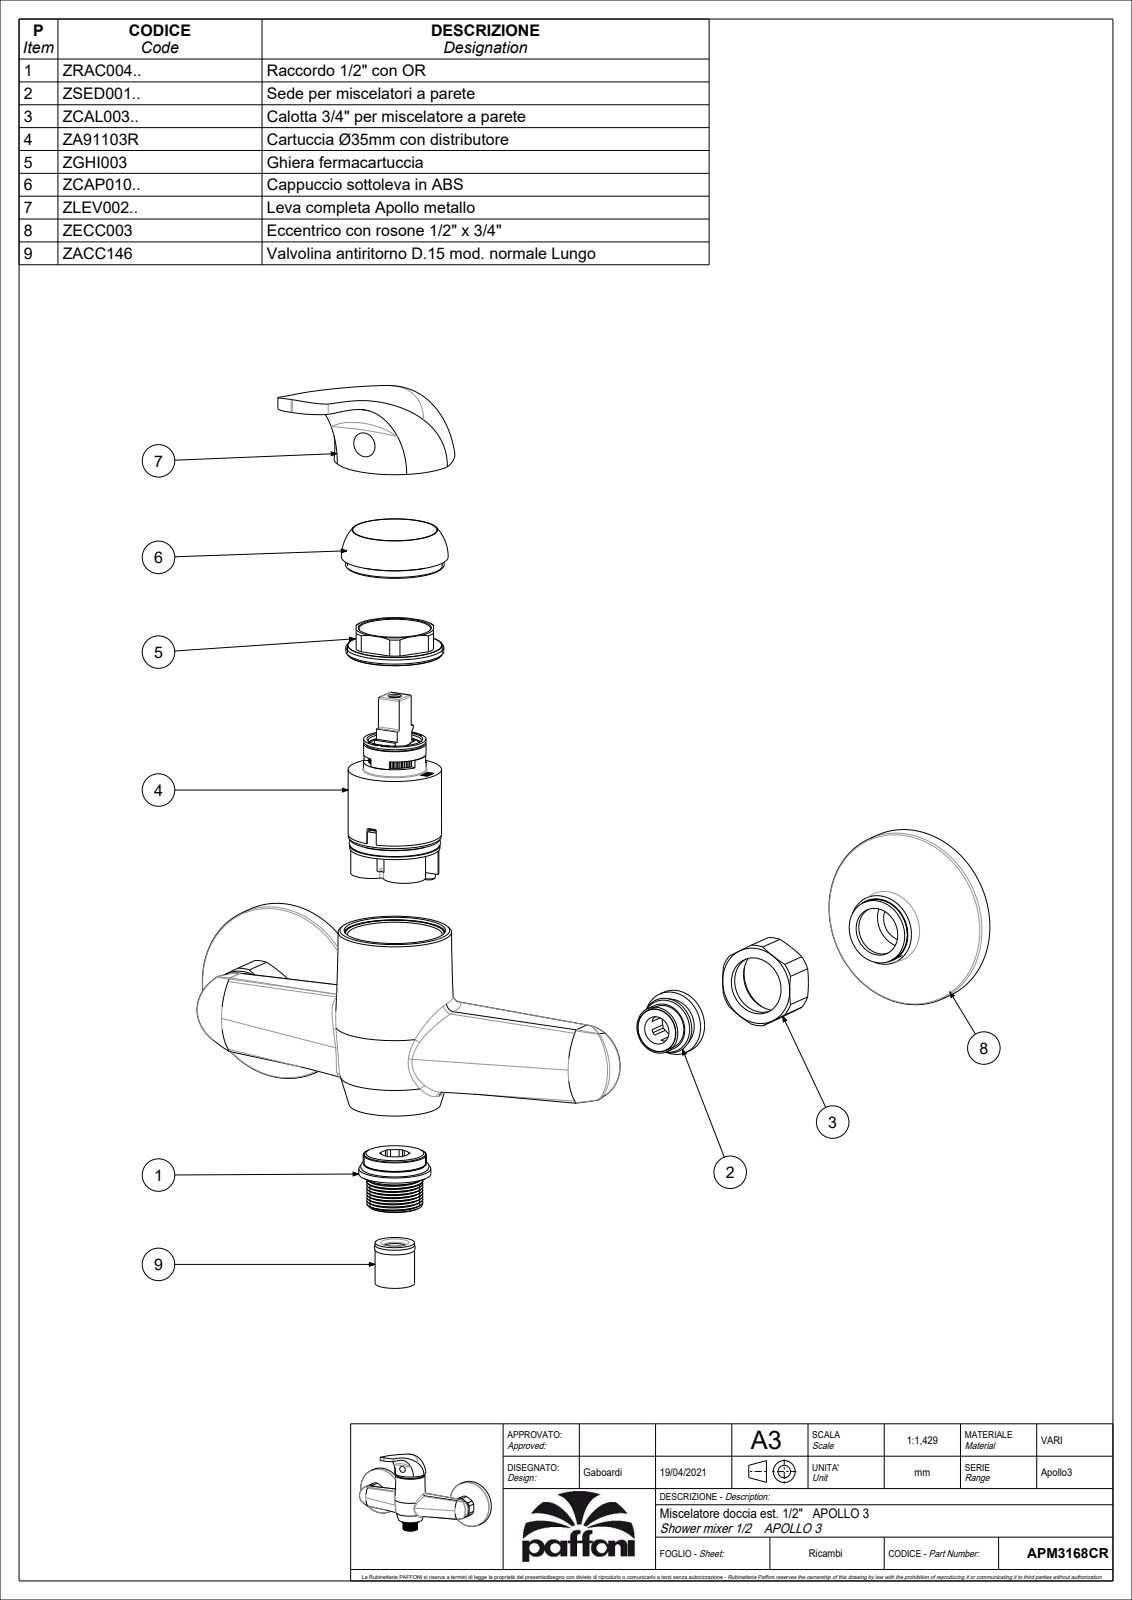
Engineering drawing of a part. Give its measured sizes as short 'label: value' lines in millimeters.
name: APM3168CR
written by: CREO PARAMETRIC BY PTC INC, 2020044 (CONFIG_CONTROL_DESIGN)
unit: mm
bodies: 3 solids, 1478 faces (707 planar, 374 cylindrical, 397 other)
size: 216 × 126.25 × 126
volume: 133 616 mm³; area: 107 770 mm²
holes: 3× ⌀9, 3× ⌀12, 2× ⌀4, 2× ⌀7, 2× ⌀8, 2× ⌀10.5, 2× ⌀18, 2× ⌀21.5, 2× ⌀24.1, 2× ⌀25, 2× ⌀26.7, 2× ⌀65.4
bosses: 2× ⌀66, 2× ⌀25.6, 2× ⌀24, 1× ⌀35, 1× ⌀34.8, 1× ⌀33.8, 1× ⌀32.2, 1× ⌀31.5
rounds: 41× R0.5, 12× R1, 11× R0.15, 9× R0.3, 4× R7, 2× R3.5, 2× R4.5, 2× R7.95
face distances: 3.5, 0.5, 3, 8.5, 6, 4.5, 9.5, 12, 9, 2.5
hole spacings: 0.71, 8.51, 8.6, 13.04, 13.21, 13.51, 89.42, 94.81
